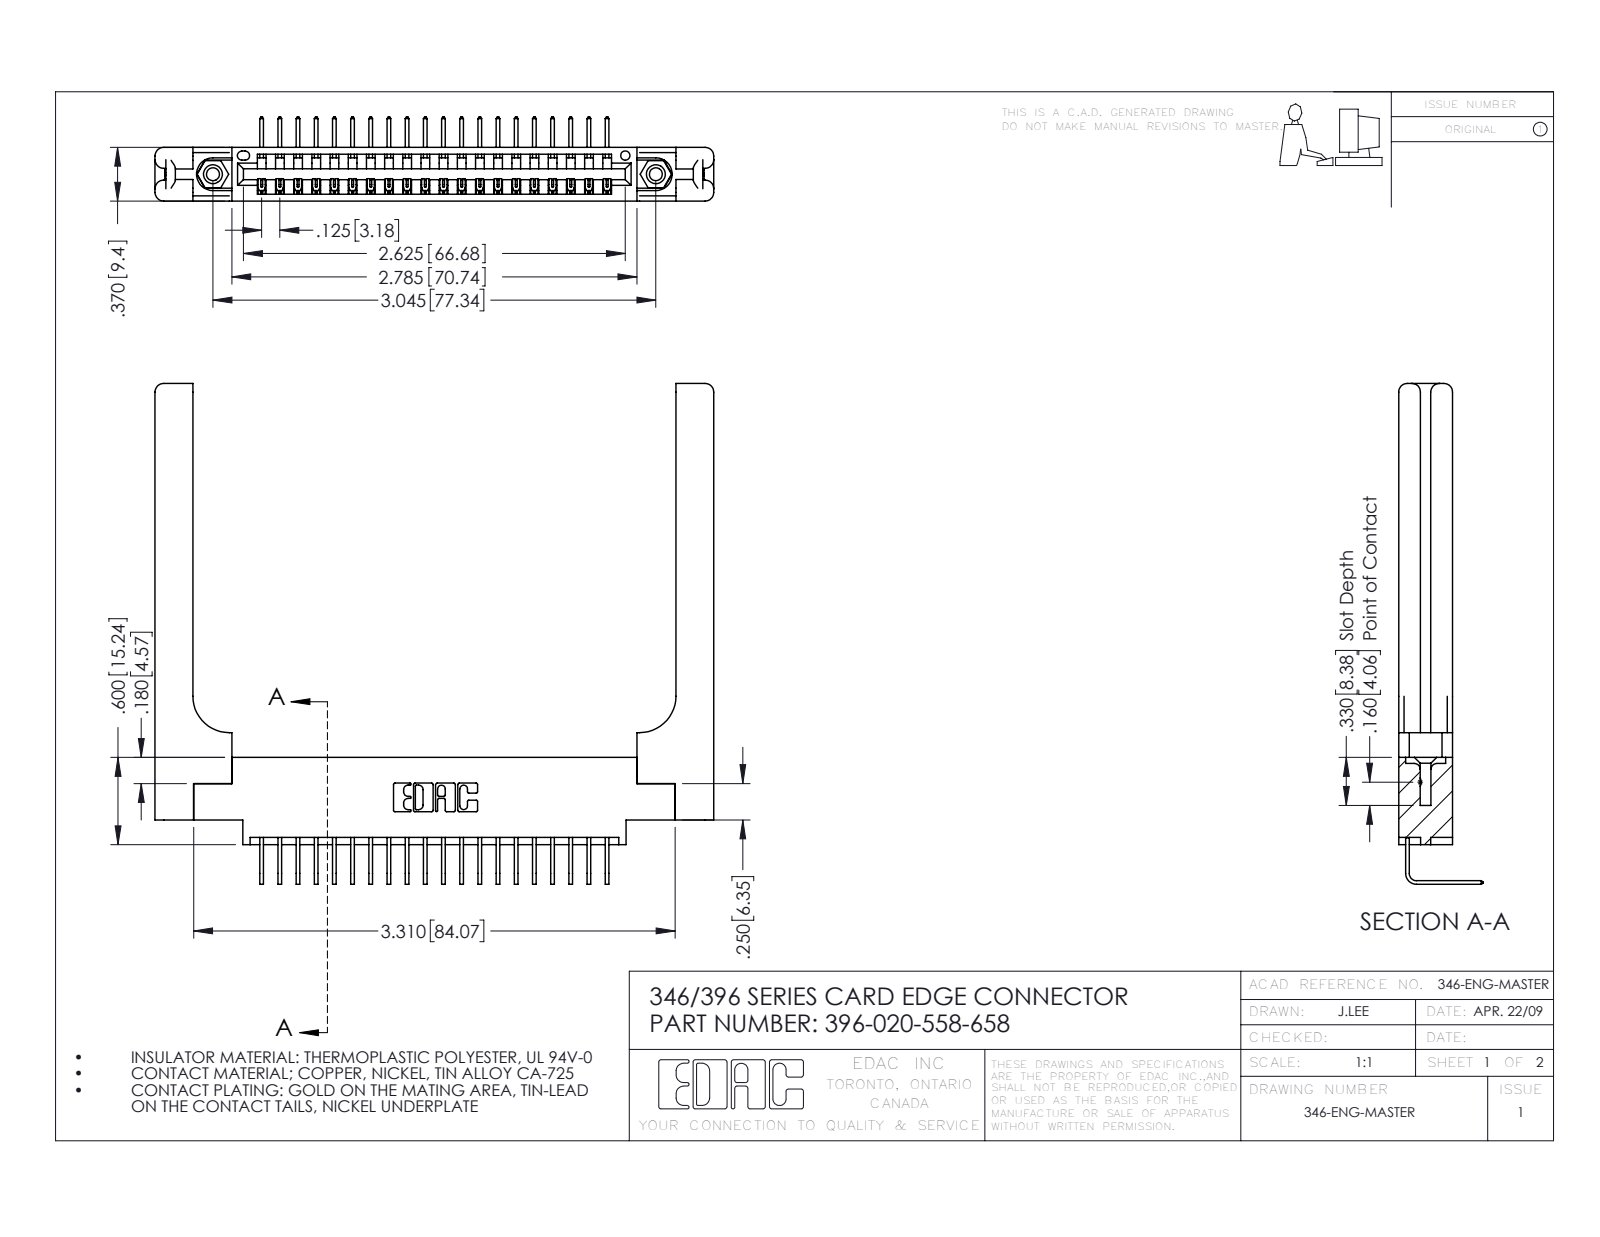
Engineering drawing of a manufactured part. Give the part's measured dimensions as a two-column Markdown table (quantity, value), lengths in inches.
| quantity | value |
| --- | --- |
| part name | 346-220-058_345-220-058; 396-020-558-658; 345-292-001_558 Tail - 2; 346 Part_0.170 Offset - 0.156 Dia-TH (+1 more) |
| STEP written by | SolidWorks 2016 (CONFIG_CONTROL_DESIGN) |
| units | inches |
| bodies | 25 solids, 1582 faces (1068 planar, 454 cylindrical, 60 other) |
| overall size | 3.841 × 3.443 × 0.58 |
| volume | 1.014 in³ |
| surface area | 26.14 in² |
| round holes (diameter × count) | 0.089 × 2, 0.125 × 2, 0.156 × 2, 0.064 × 1 |
| round bosses / shafts (diameter × count) | 0.155 × 2 |
| partial cylindrical surfaces (radius × count) | 0.006 × 40, 0.01 × 22, 0.06 × 16, 0.007 × 6, 0.031 × 6, 0.026 × 3, 0.03 × 2, 0.031 × 2 |
| main face-to-face distances | 0.37, 0.072, 0.322, 0.15, 0.148, 0.048, 0.25, 0.025, 0.298, 0.102 |
| hole center spacings | 0.246, 2.837, 3.045 |
